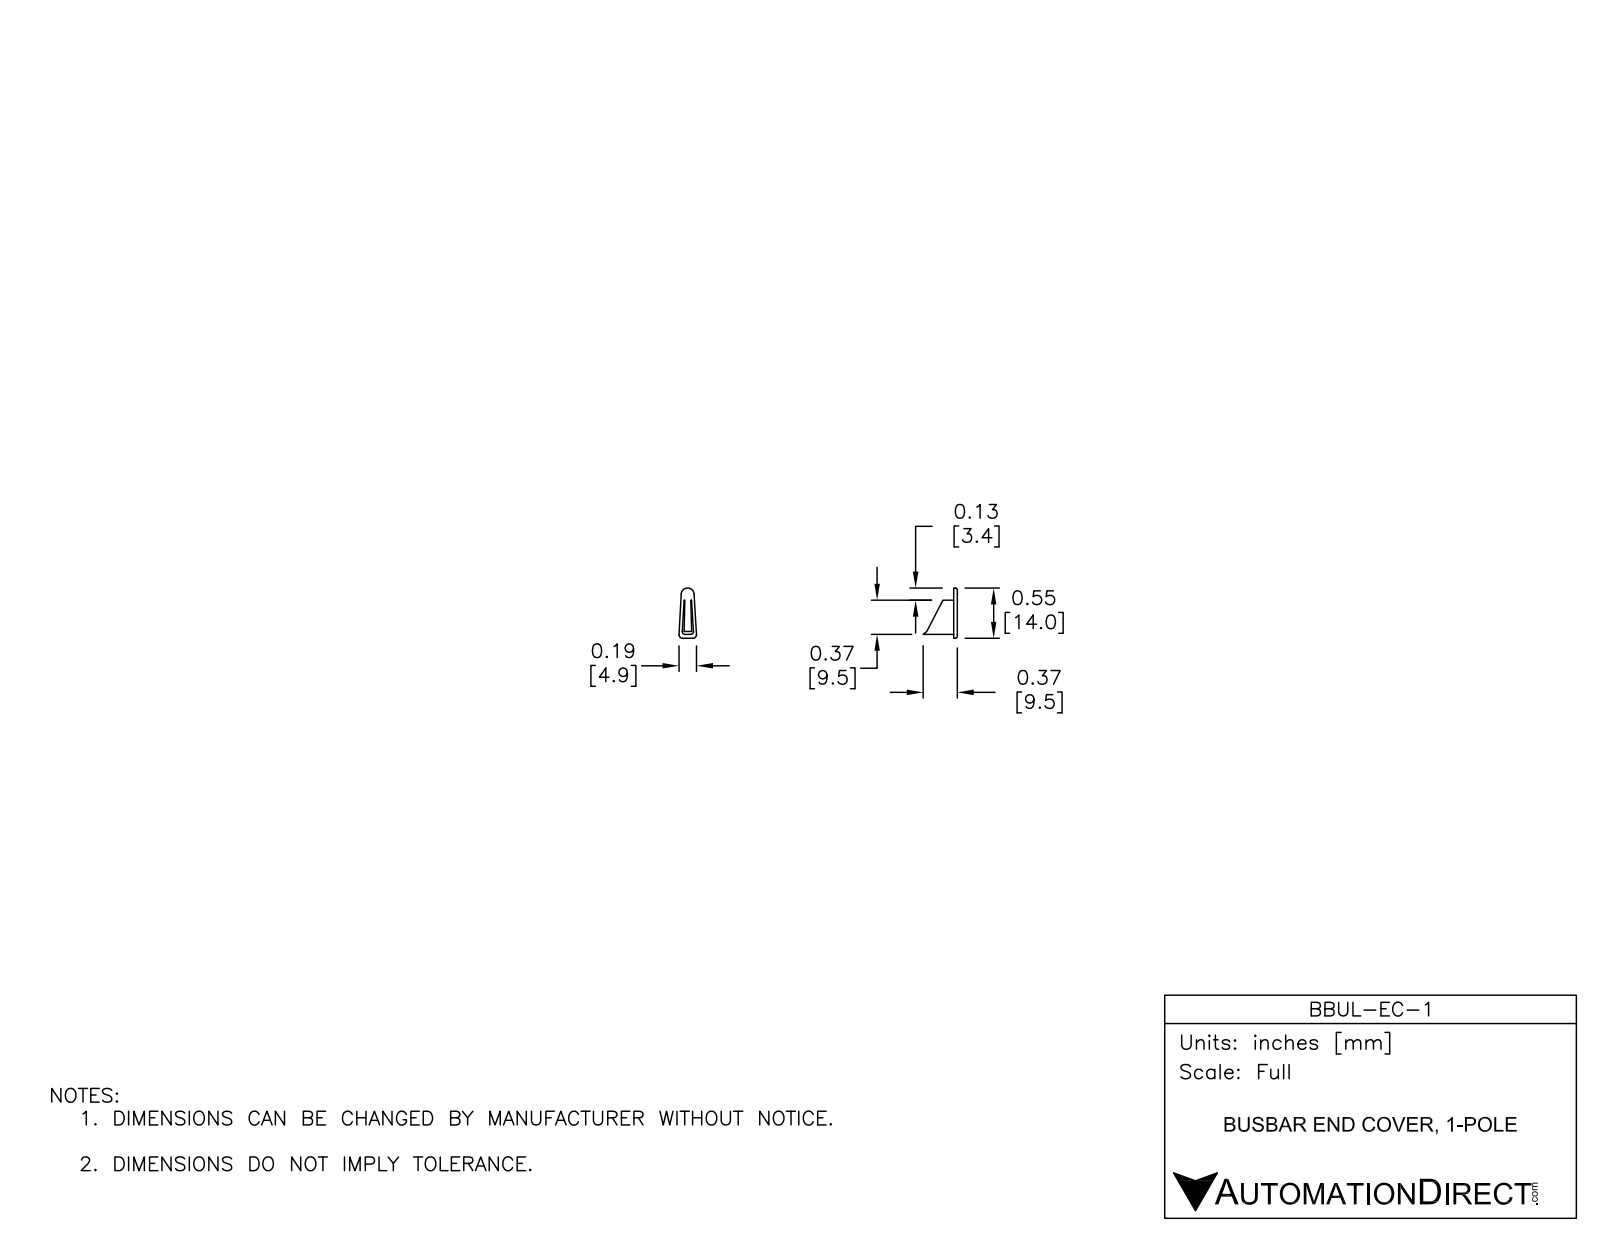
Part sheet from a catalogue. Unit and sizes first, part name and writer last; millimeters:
Units: millimetres
Overall size (bounding box): 13.51 × 9.5 × 4.88
Partial cylindrical surfaces — rounded edges, fillets, slot ends (radius × count): R0.7 ×5, R1 ×2, R1.8 ×1
Main face-to-face distances: 1, 0.8, 9.5, 8.7, 1.1, 1.9, 10.6
Volume: 104 mm³ · Surface area: 369 mm²
Bodies: 1 solid, 31 faces (16 planar, 10 cylindrical, 5 other)
Part name (STEP PRODUCT): BBUL-EC-1
STEP written by: SolidWorks 2014 (AUTOMOTIVE_DESIGN)
